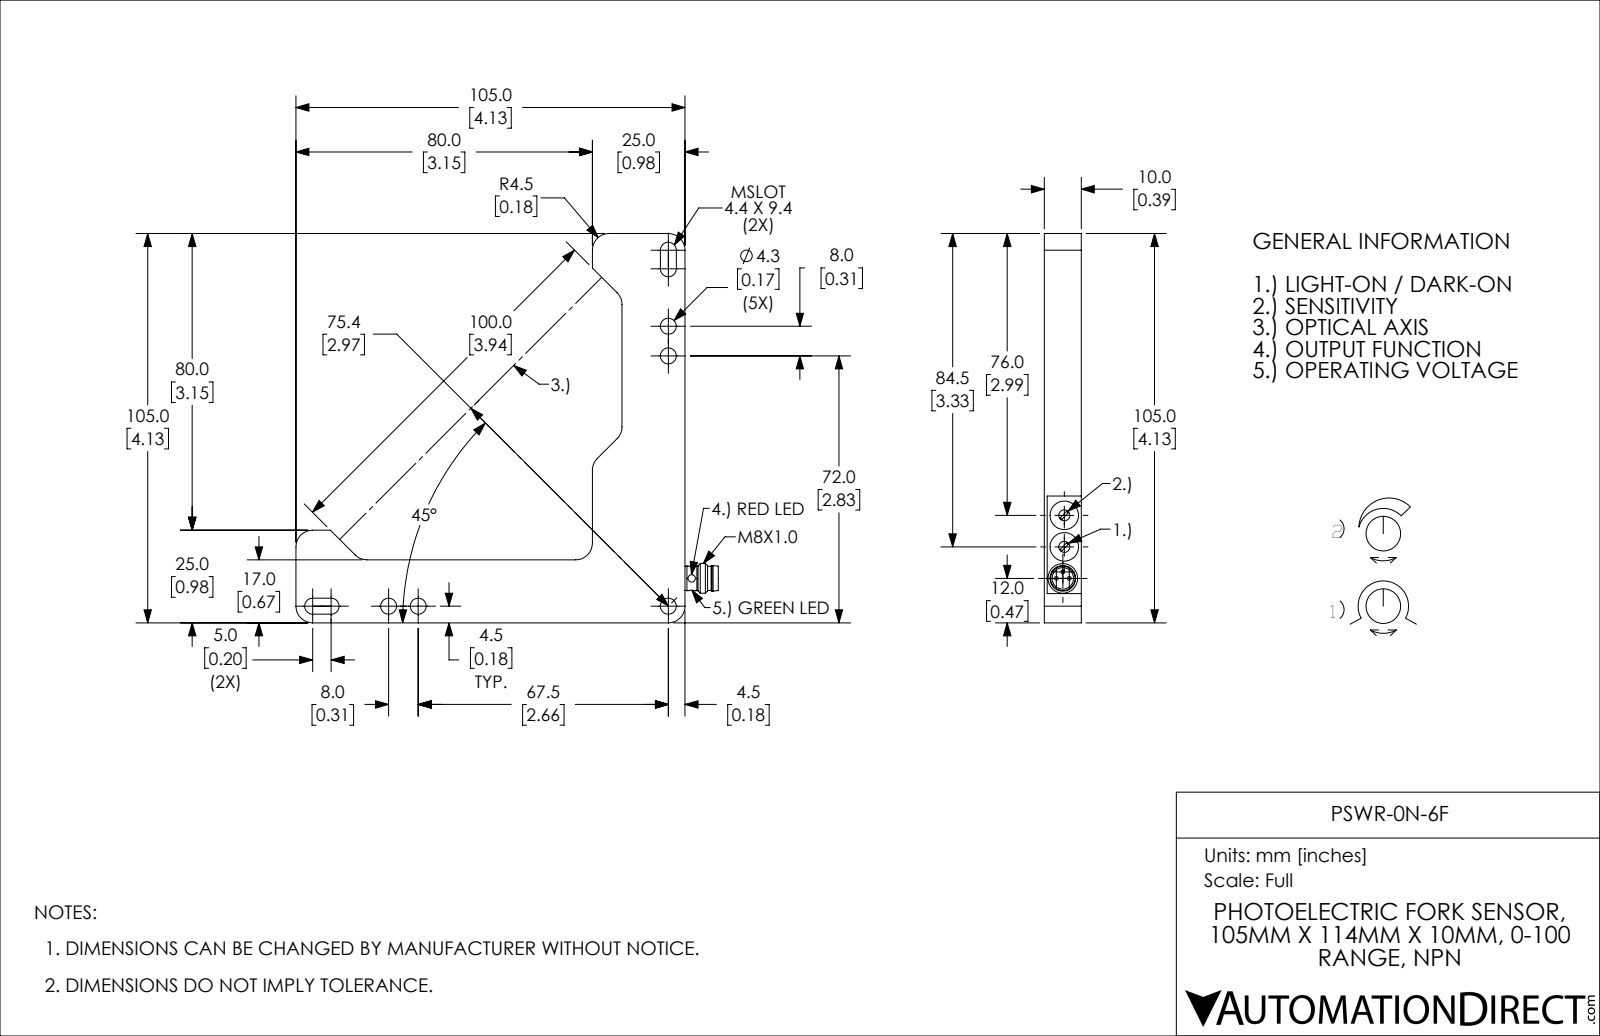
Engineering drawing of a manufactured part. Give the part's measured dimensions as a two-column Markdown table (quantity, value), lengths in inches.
| quantity | value |
| --- | --- |
| part name | PSWR-0N-6F |
| STEP written by | SolidWorks 2017 (AUTOMOTIVE_DESIGN) |
| units | inches |
| bodies | 1 solid, 90 faces (42 planar, 41 cylindrical, 7 other) |
| overall size | 4.488 × 4.134 × 0.394 |
| volume | 2.191 in³ |
| surface area | 20.03 in² |
| round holes (diameter × count) | 0.169 × 5, 0.079 × 2, 0.118 × 2, 0.303 × 2, 0.228 × 1 |
| round bosses / shafts (diameter × count) | 0.039 × 3, 0.315 × 1, 0.272 × 1, 0.264 × 1, 0.257 × 1 |
| partial cylindrical surfaces (radius × count) | 0.177 × 10, 0.085 × 4, 0.049 × 2 |
| main face-to-face distances | 0.394, 0.669, 4.134, 3.465, 0.984, 0.315, 3.15, 4.13, 0.98, 0.665 |
| hole center spacings | 0.315, 2.657, 2.972, 3.987, 0.335, 0.335, 0.385, 0.669 |
